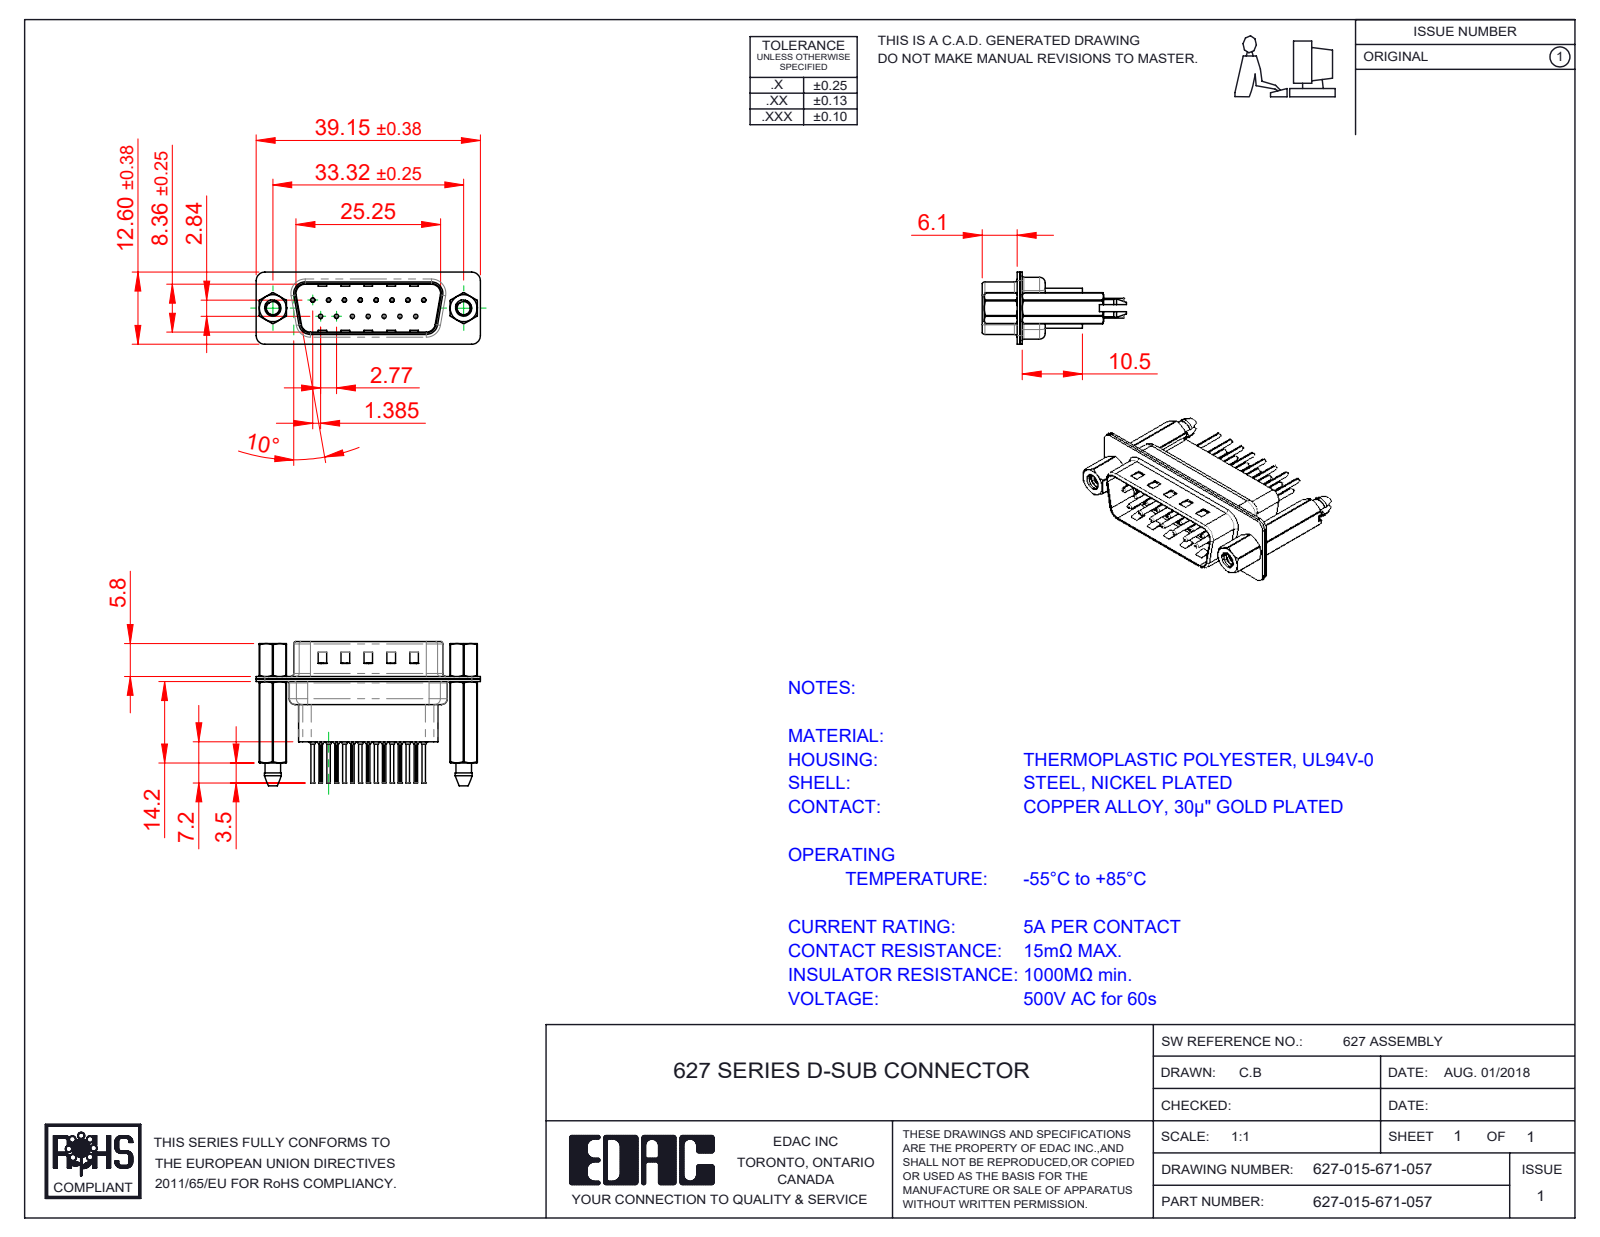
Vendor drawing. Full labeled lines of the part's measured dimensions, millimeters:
Part name (STEP PRODUCT): 627 Shell Front_15 Contacts; 627 Contact Row 1_61; 627-015-671-057; 627 Shell Rear_15 Contacts (+4 more)
STEP written by: SolidWorks 2020 (CONFIG_CONTROL_DESIGN)
Units: millimetres
Bodies: 22 solids, 2044 faces (553 planar, 826 cylindrical, 665 other)
Overall size (bounding box): 39.15 × 25.1 × 12.6
Volume: 3 123 mm³ · Surface area: 8 000 mm²
Round holes (diameter × count): ⌀0.2 ×15, ⌀0.35 ×15, ⌀1.1 ×15, ⌀1.6 ×15, ⌀2.26 ×2, ⌀2.29 ×2, ⌀4 ×2, ⌀4.8 ×2
Round bosses / shafts (diameter × count): ⌀2 ×15, ⌀1.5 ×15, ⌀0.75 ×15, ⌀0.6 ×15, ⌀4.9 ×2, ⌀2.79 ×2
Partial cylindrical surfaces — rounded edges, fillets, slot ends (radius × count): R0.1 ×30, R1.5 ×18, R2 ×12, R1.6 ×10, R0.5 ×8, R0.25 ×4, R0.6 ×4, R0.65 ×4
Main face-to-face distances: 0.4, 0.45, 4.76, 0.9, 0.82, 9.58, 1.5, 0.68, 7.68, 16.66
Hole centre spacings: 3.16, 2.77, 5.54, 8.31, 11.08, 5.03, 5.04, 7.48
